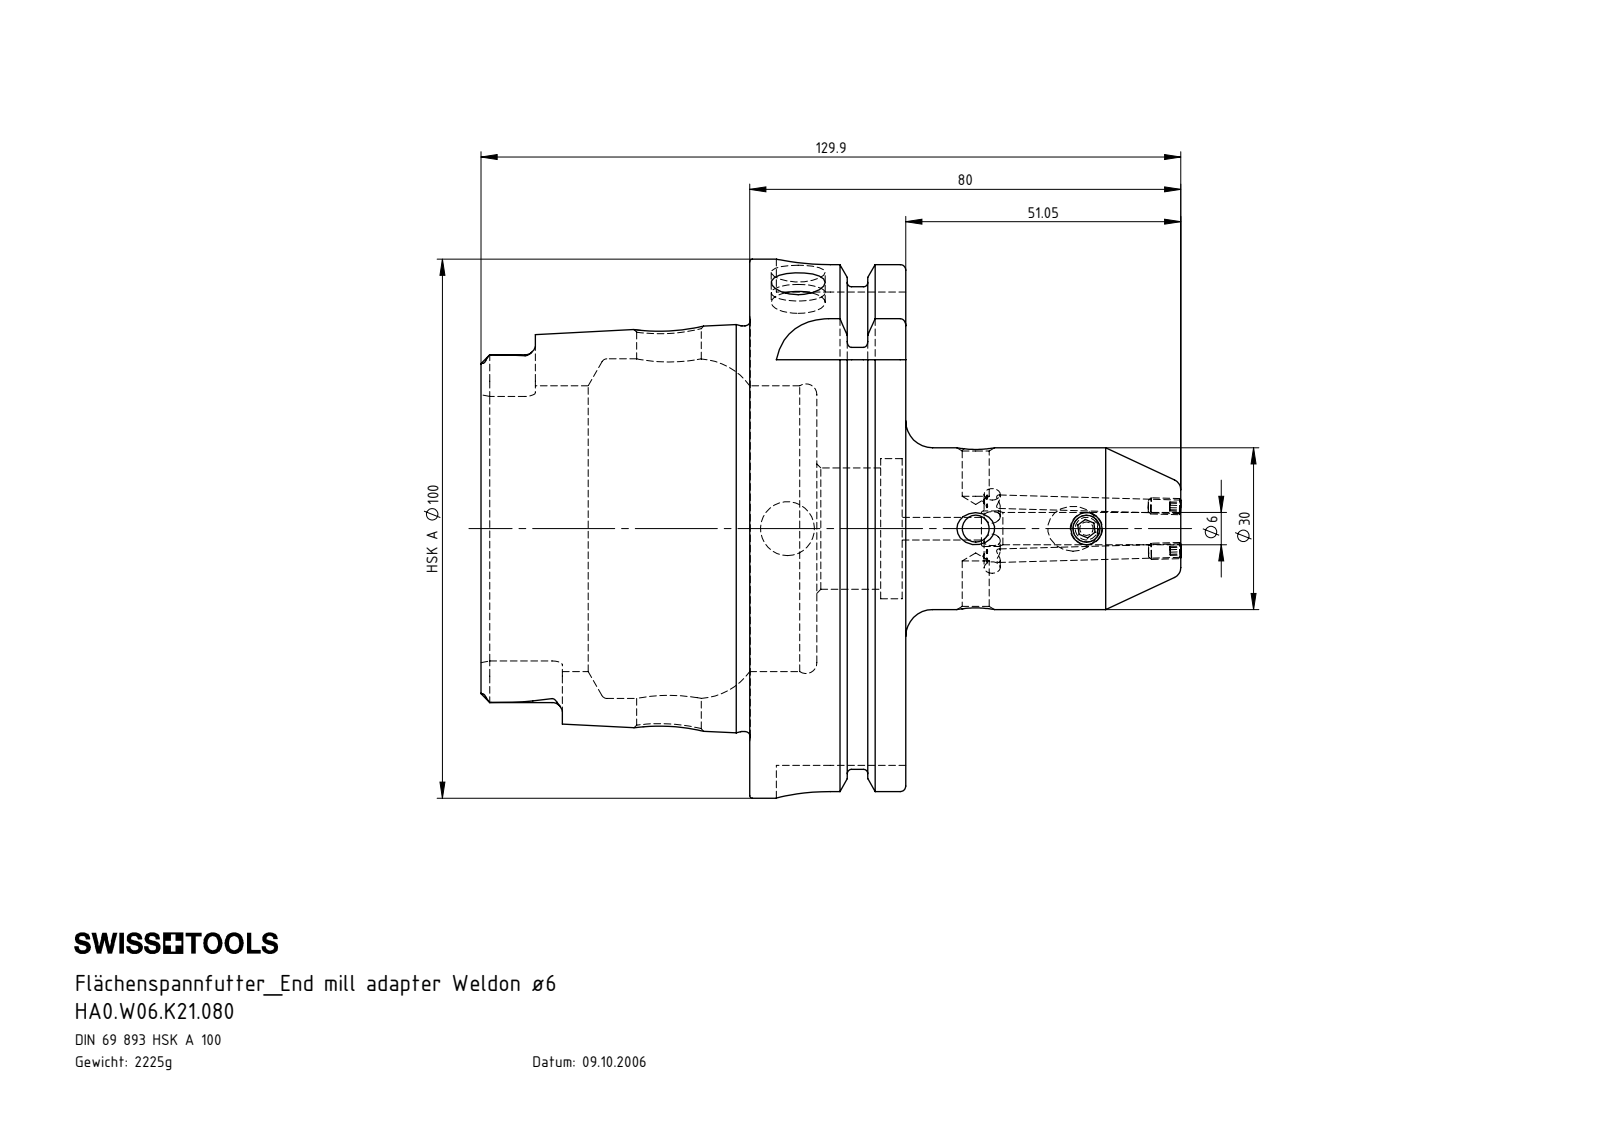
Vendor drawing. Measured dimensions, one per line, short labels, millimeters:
name: HA0.W06.K21.080; ERU-CJ2.001.006; W06-ER1.001.010; HA0-W06.K21.080_C_Fertigbearbeitung
written by: SolidWorks 2012 (CONFIG_CONTROL_DESIGN)
unit: mm
bodies: 4 solids, 271 faces (71 planar, 82 cylindrical, 118 other)
size: 129.98 × 100 × 100
volume: 283 399 mm³; area: 56 467 mm²
holes: 3× ⌀5, 3× ⌀10, 2× ⌀2.5, 1× ⌀3, 1× ⌀4.2, 1× ⌀6, 1× ⌀6.6, 1× ⌀12, 1× ⌀22.5, 1× ⌀26, 1× ⌀53, 1× ⌀63
bosses: 2× ⌀3, 1× ⌀100, 1× ⌀91.95, 1× ⌀75.26, 1× ⌀30, 1× ⌀6
rounds: 6× R1.9, 4× R4.88, 4× R10
face distances: 28.95, 12.45, 16.5, 49.9, 62.35, 78.85, 78.2, 28.3, 15.85, 0.65
hole spacings: 20.55, 34.95, 55.5, 56.95
